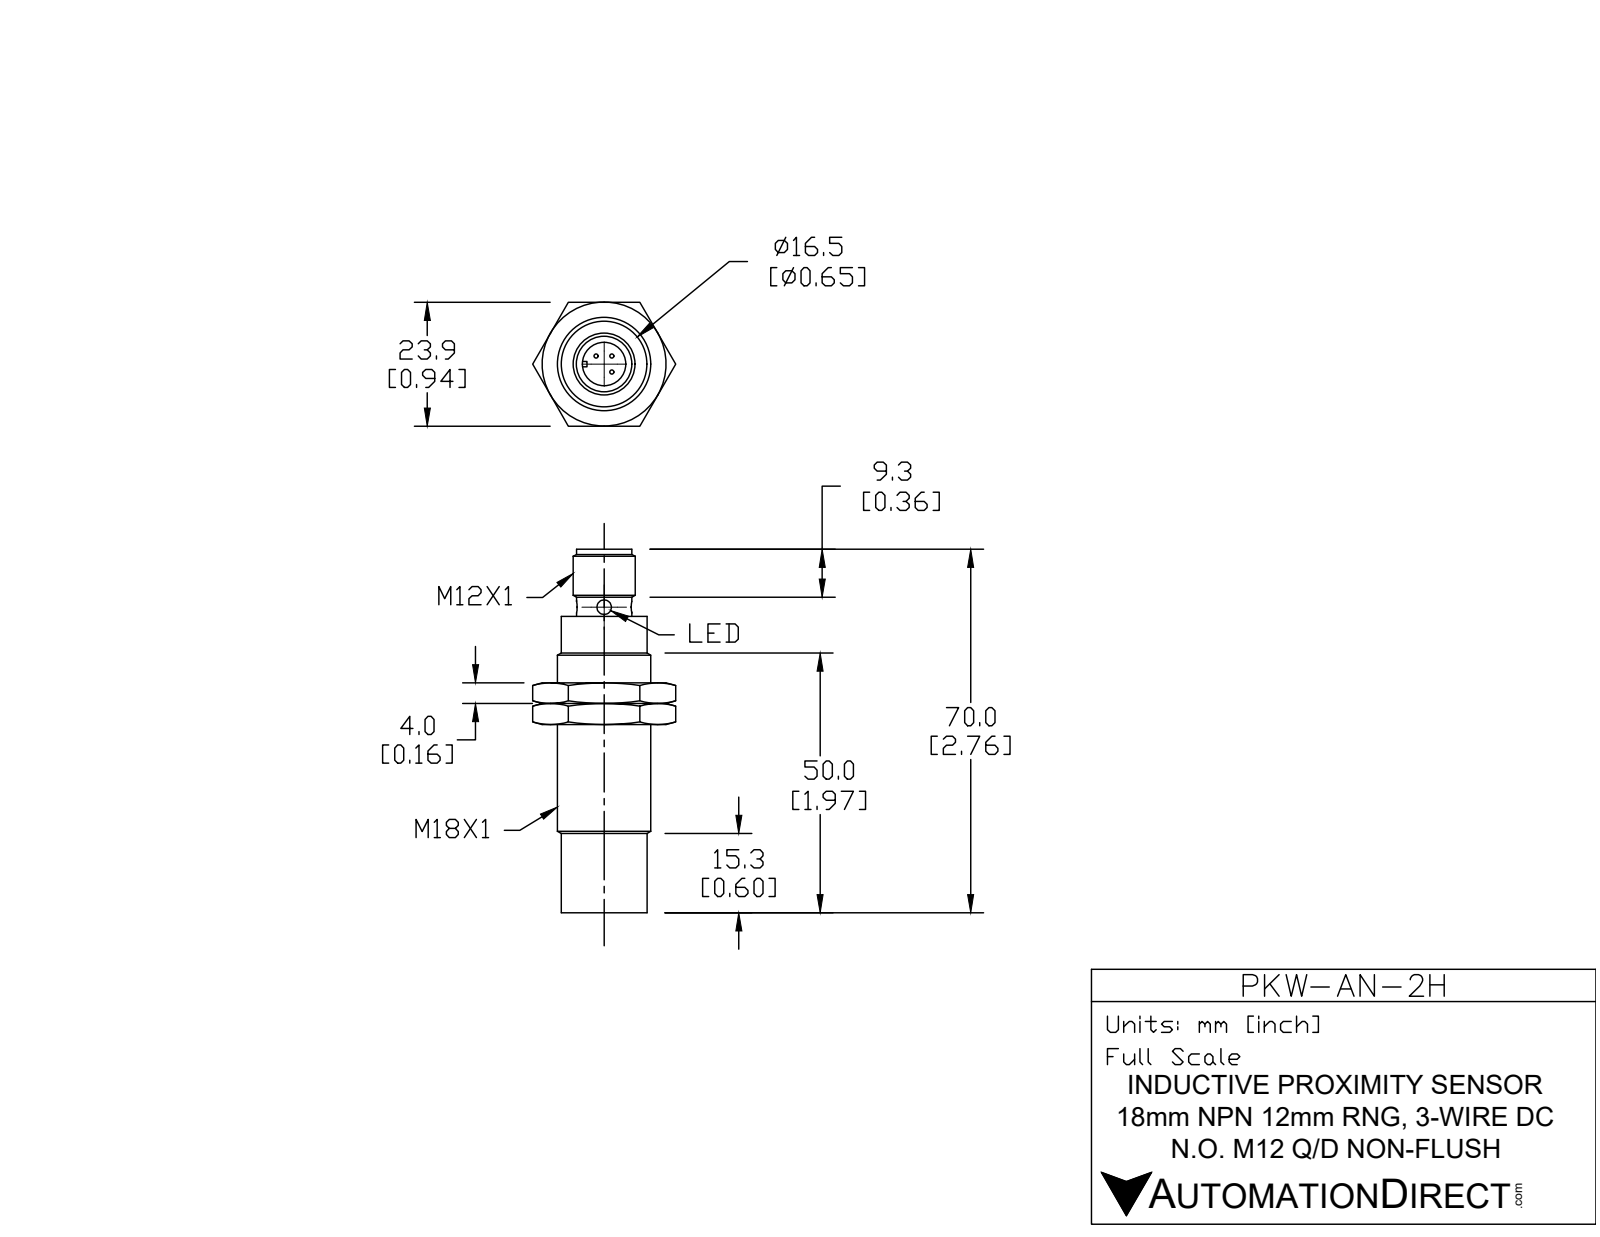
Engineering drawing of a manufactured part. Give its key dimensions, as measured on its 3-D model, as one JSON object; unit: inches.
{"part_name": "PKW-AN-2H", "step_written_by": "SolidWorks 2017 (AUTOMOTIVE_DESIGN)", "units": "inches", "bodies": {"solids": 3, "faces": 124, "planar": 26, "cylindrical": 27, "other": 71}, "overall_size": [2.764, 1.091, 0.945], "volume_in3": 1.015, "surface_area_in2": 9.927, "round_holes": [[0.118, 2], [0.331, 1], [0.666, 1]], "round_bosses_or_shafts": [[0.709, 1], [0.654, 1], [0.652, 1], [0.472, 1], [0.445, 1], [0.417, 1]], "partial_cylinders_radius": [[0.024, 1]], "face_to_face_distances": [0.157, 0.945, 0.953, 0.315, 1.11, 0.795, 1.299, 1.457, 1.142, 2.252]}
